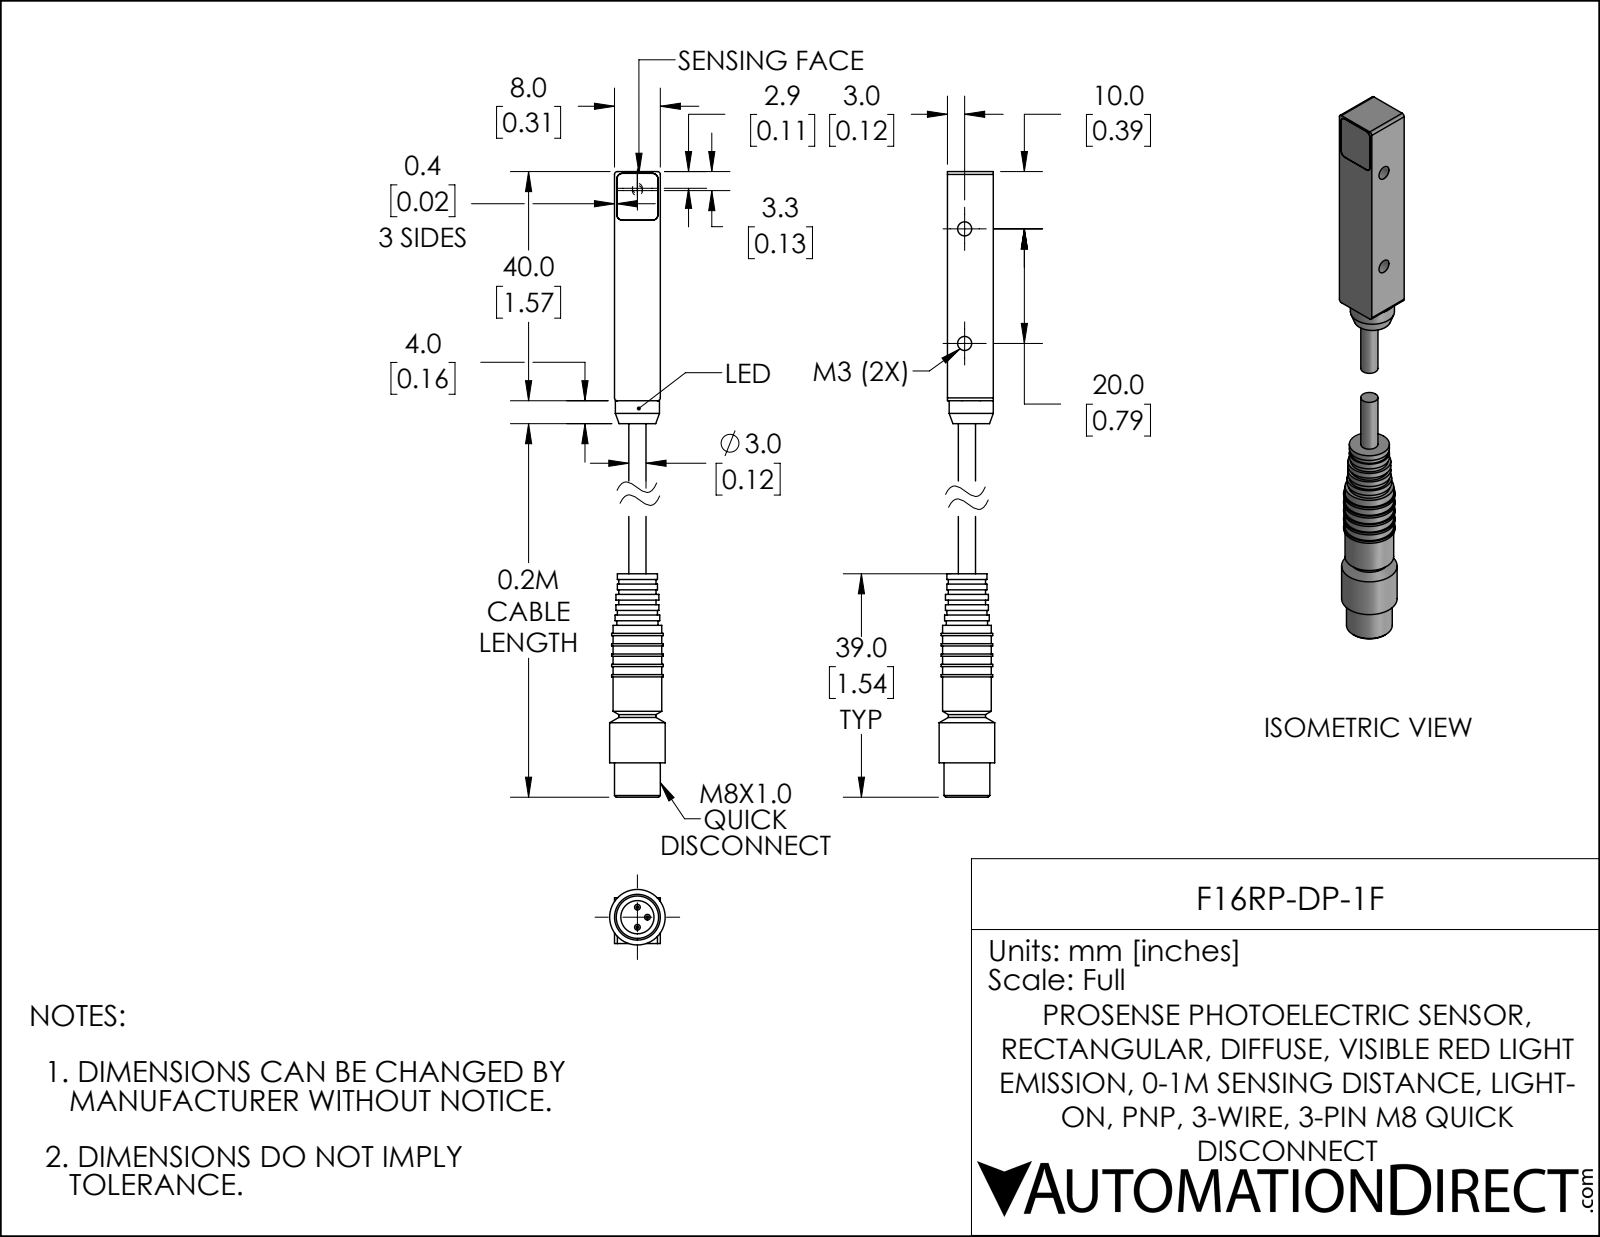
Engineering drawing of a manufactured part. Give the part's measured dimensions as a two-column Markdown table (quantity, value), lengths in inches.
| quantity | value |
| --- | --- |
| part name | F16RP-DP-1F_2; F16RP-DP-1F_1; F16RP-DP-1F |
| STEP written by | SolidWorks 2019 (AUTOMOTIVE_DESIGN) |
| units | inches |
| bodies | 2 solids, 102 faces (50 planar, 45 cylindrical, 7 other) |
| overall size | 4.358 × 0.382 × 0.382 |
| volume | 0.293 in³ |
| surface area | 5.017 in² |
| round holes (diameter × count) | 0.097 × 2, 0.228 × 1 |
| round bosses / shafts (diameter × count) | 0.039 × 3, 0.382 × 1, 0.354 × 1, 0.335 × 1, 0.315 × 1, 0.307 × 1, 0.303 × 1, 0.295 × 1 |
| partial cylindrical surfaces (radius × count) | 0.02 × 4, 0.039 × 4, 0.039 × 4 |
| main face-to-face distances | 0.315, 0.071, 0.142, 0.039, 0.354, 1.732, 2.823, 2.429, 0.213, 1.091 |
| hole center spacings | 0.787 |
